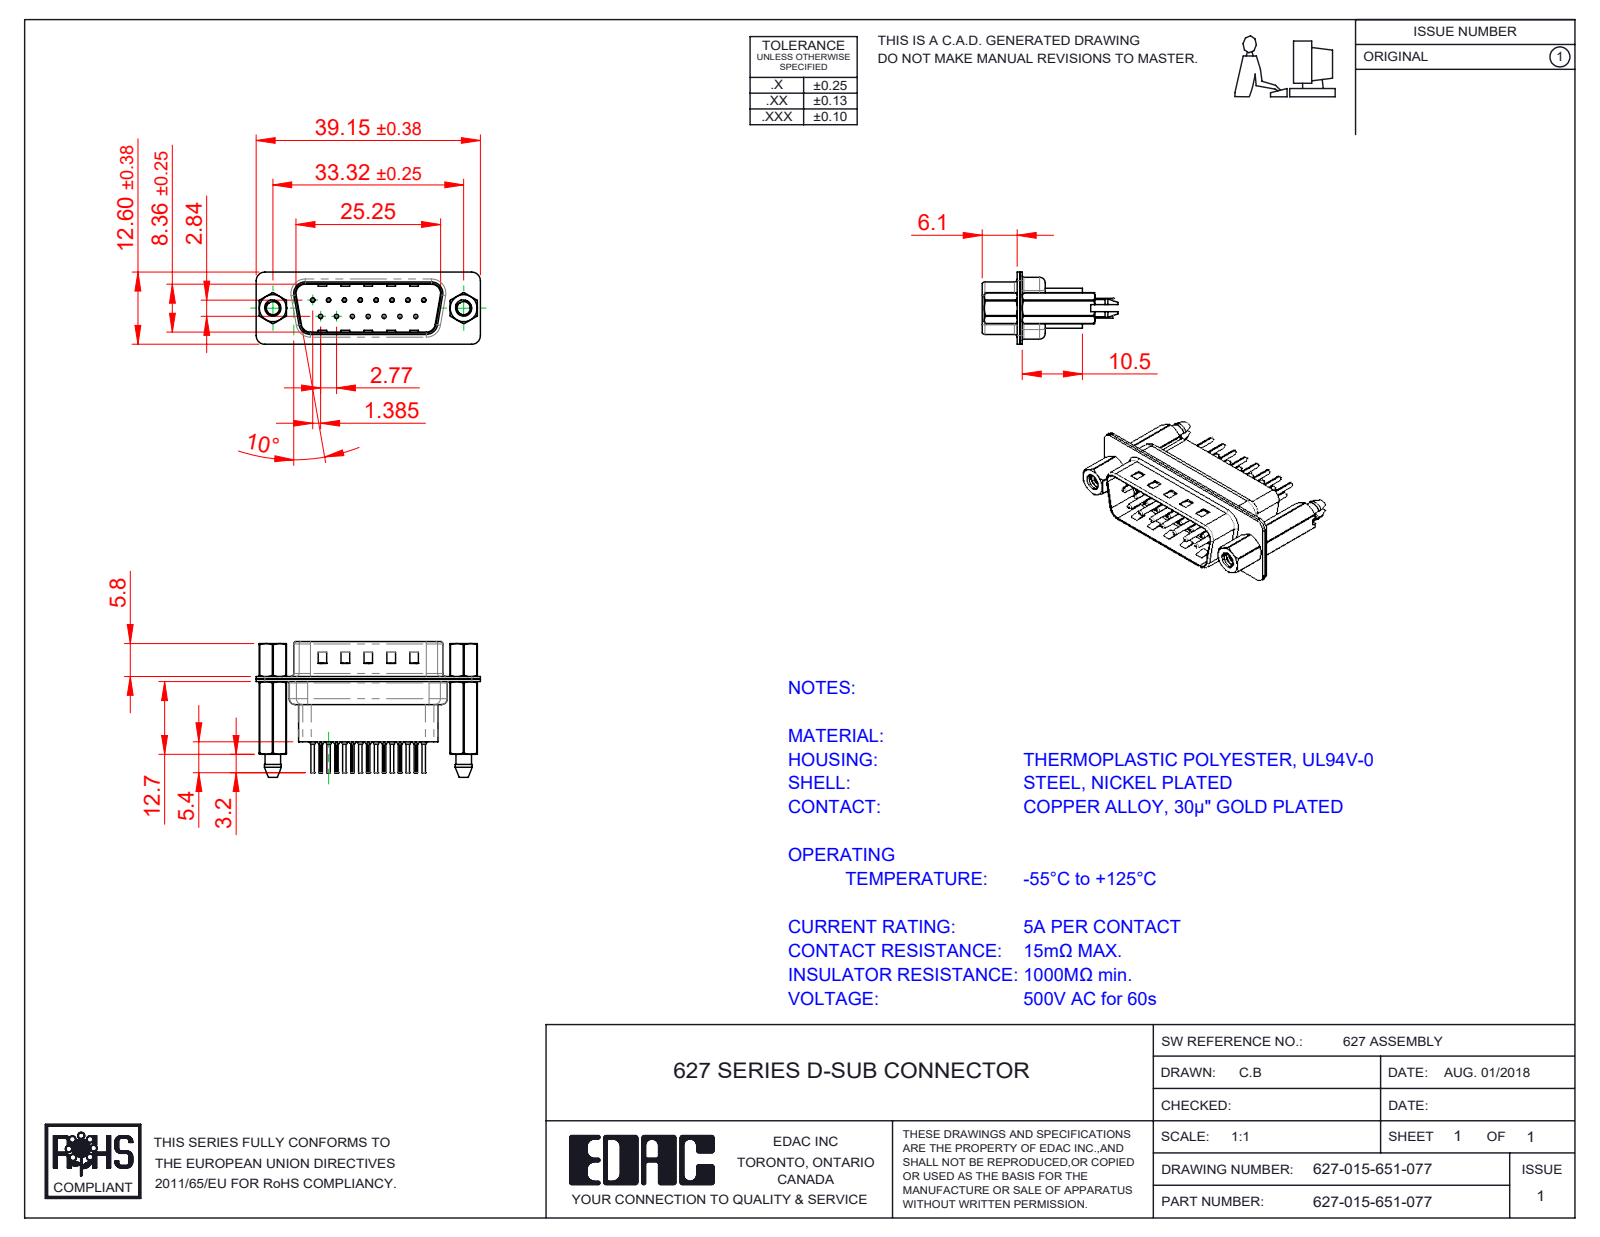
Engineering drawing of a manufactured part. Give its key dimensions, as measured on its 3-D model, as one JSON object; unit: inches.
{"part_name": "627 Housing_15 HP; 627 Contact Row 1_41; 627 Shell Front_15 Contacts; 627 Contact Row 2_41 (+4 more)", "step_written_by": "SolidWorks 2020 (CONFIG_CONTROL_DESIGN)", "units": "inches", "bodies": {"solids": 22, "faces": 2044, "planar": 553, "cylindrical": 826, "other": 665}, "overall_size": [1.541, 0.929, 0.496], "volume_in3": 0.187, "surface_area_in2": 12.17, "round_holes": [[0.008, 15], [0.014, 15], [0.043, 15], [0.063, 15], [0.089, 2], [0.09, 2], [0.157, 2], [0.189, 2]], "round_bosses_or_shafts": [[0.079, 15], [0.059, 15], [0.03, 15], [0.024, 15], [0.193, 2], [0.11, 2]], "partial_cylinders_radius": [[0.004, 30], [0.059, 18], [0.079, 12], [0.063, 10], [0.02, 8], [0.01, 4], [0.024, 4], [0.026, 4]], "face_to_face_distances": [0.016, 0.018, 0.187, 0.035, 0.032, 0.377, 0.059, 0.027, 0.302, 0.055], "hole_center_spacings": [0.124, 0.109, 0.218, 0.327, 0.436, 0.198, 0.198, 0.294]}
